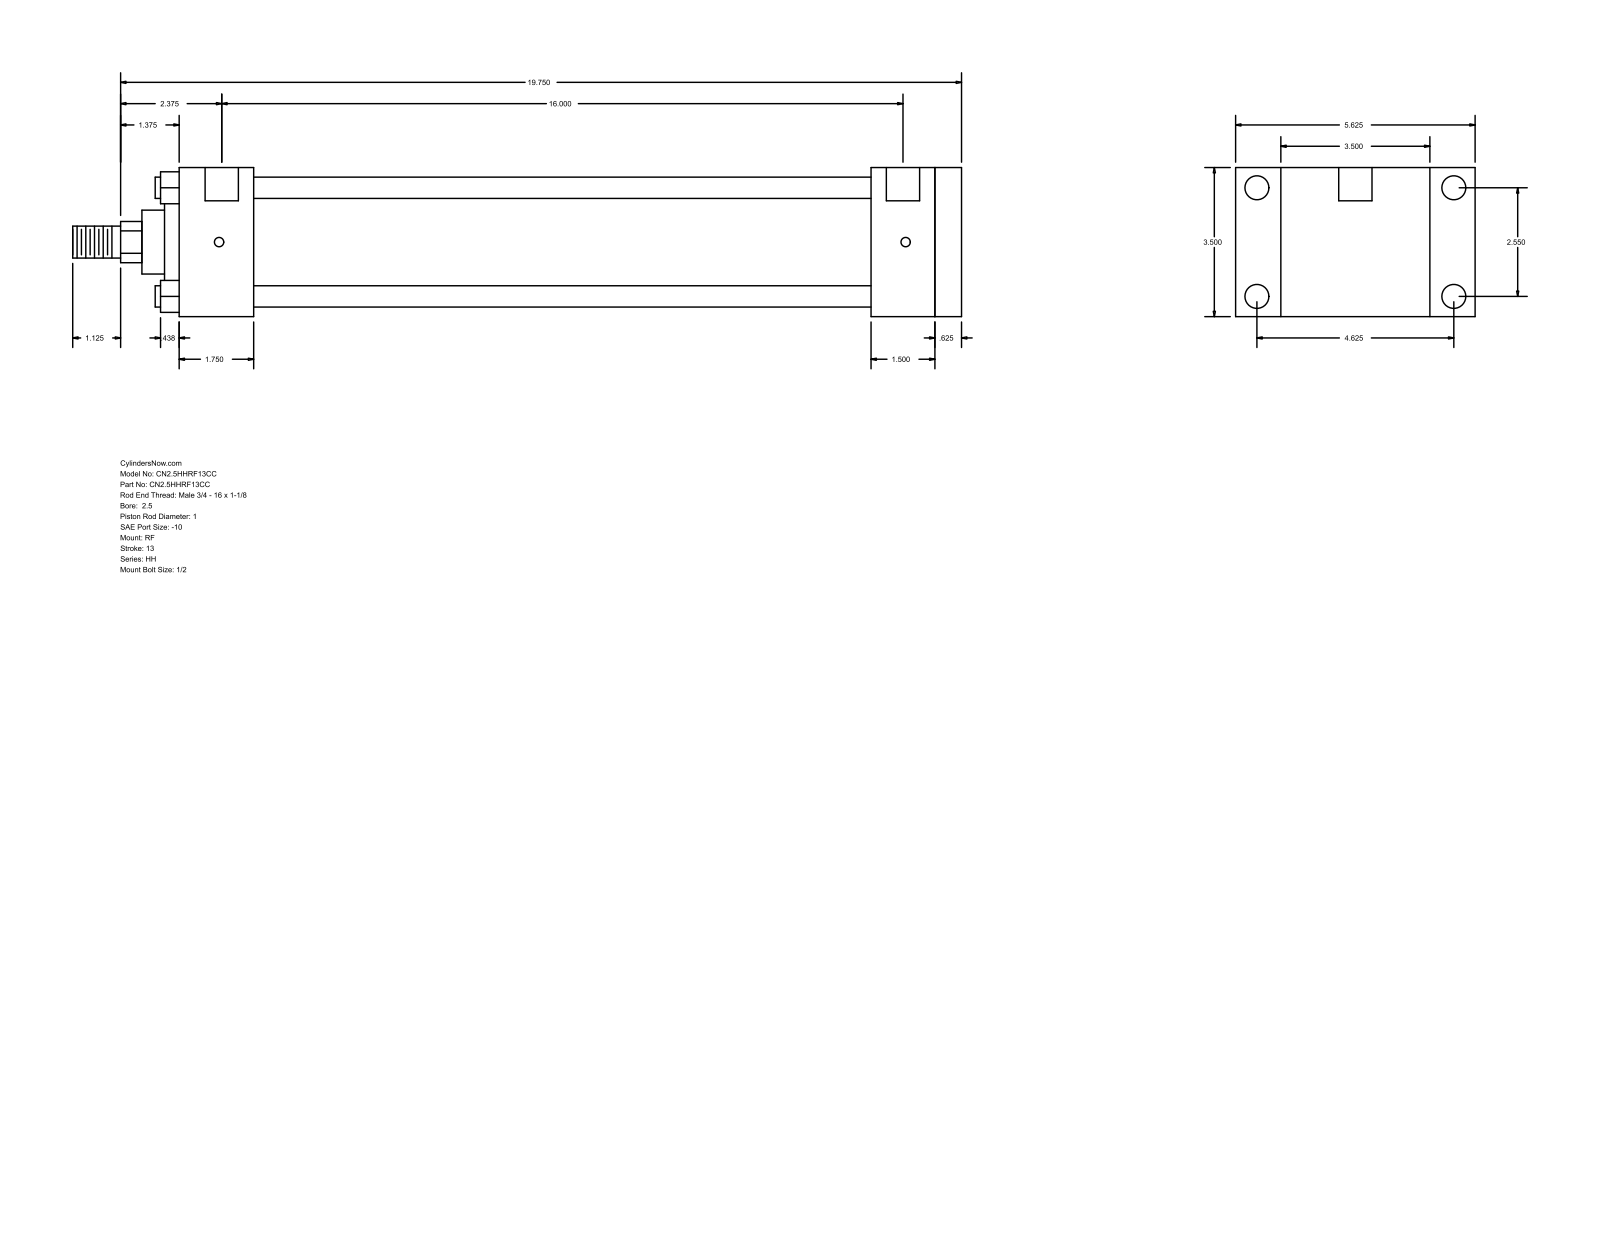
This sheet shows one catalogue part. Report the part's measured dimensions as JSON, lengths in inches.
{"part_name": "HH_RF__0250_1", "step_written_by": "GSSL Pune (CONFIG_CONTROL_DESIGN)", "units": "inches", "bodies": {"solids": 0, "faces": 94, "planar": 65, "cylindrical": 29, "other": 0}, "overall_size": [20.875, 5.625, 3.5], "round_holes": [[0.219, 4], [0.563, 4], [0.781, 2]], "round_bosses_or_shafts": [[0.5, 4], [2.875, 1], [2.375, 1], [1.5, 1], [1, 1], [0.75, 1]], "partial_cylinders_radius": [[0.484, 1]], "face_to_face_distances": [3.5, 0.625, 17.75, 18.375, 1.75, 16, 16.625, 16.25, 14.5, 1.5], "hole_center_spacings": [2.55, 4.625, 5.281, 16.125, 0.062, 0.063, 16, 16.062]}
